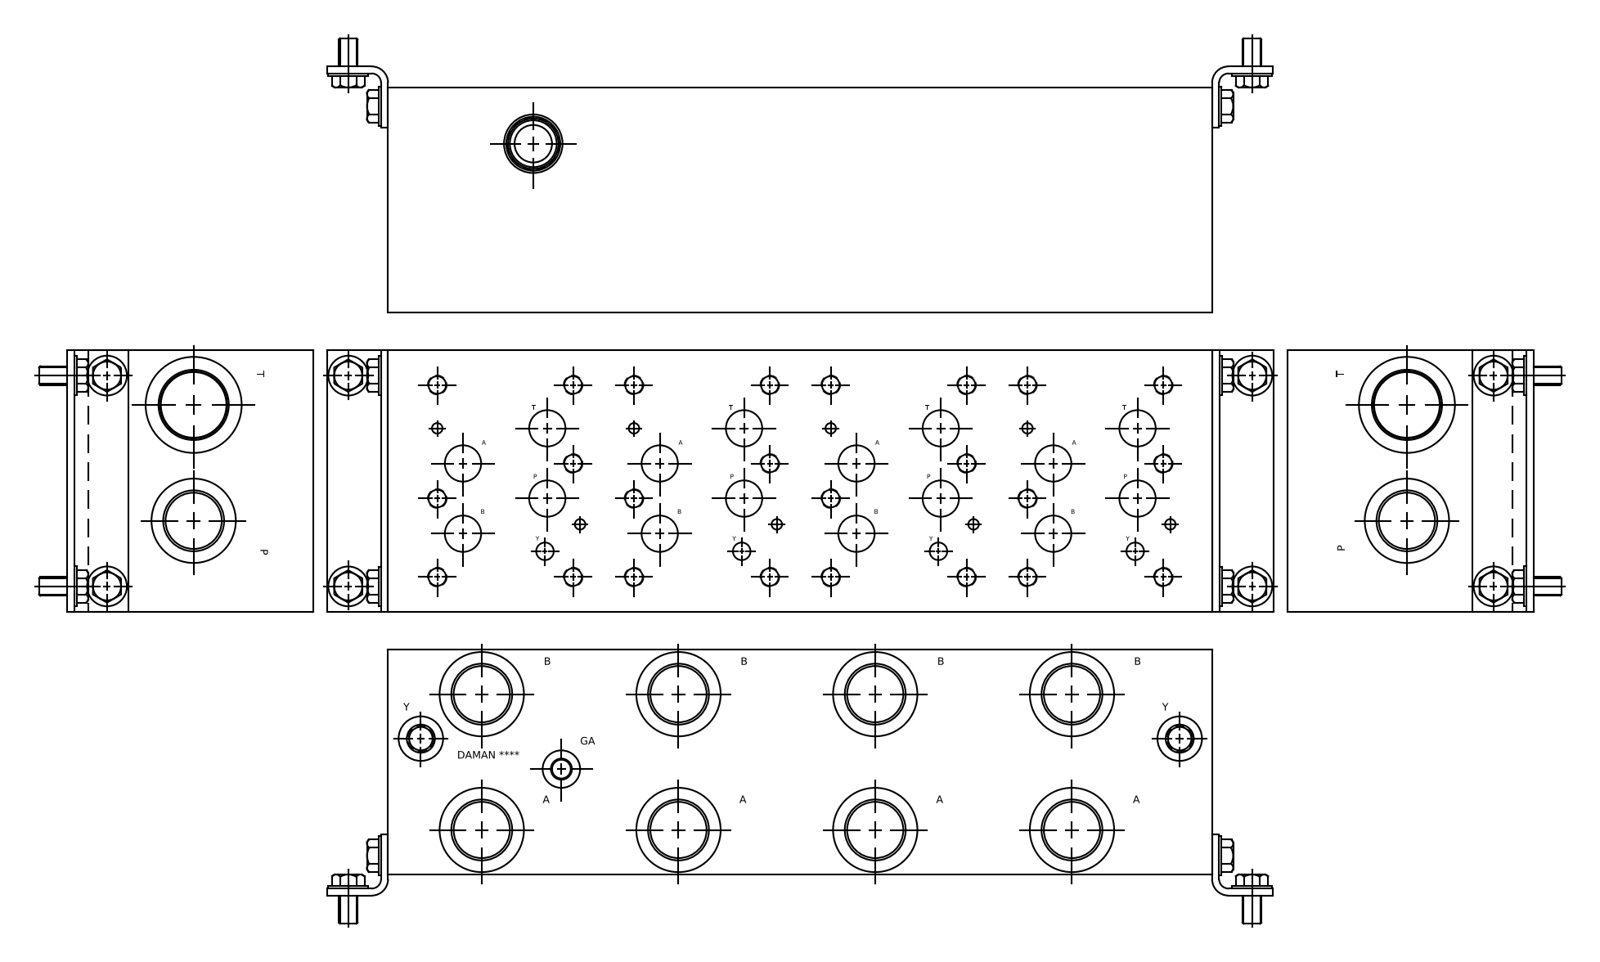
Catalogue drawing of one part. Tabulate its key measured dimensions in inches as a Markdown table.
| quantity | value |
| --- | --- |
| part name | Part_AD08HP045S~S_3D |
| STEP written by | Autodesk Inventor 2019 (AUTOMOTIVE_DESIGN) |
| units | inches |
| bodies | 1 solid, 977 faces (485 planar, 171 cylindrical, 321 other) |
| overall size | 22 × 7 × 6 |
| volume | 867.1 in³ |
| surface area | 853.7 in² |
| round holes (diameter × count) | 0.5 × 27, 0.422 × 26, 0.906 × 16, 1.544 × 9, 2.306 × 9, 0.281 × 8, 1.453 × 8, 1.625 × 8, 1.713 × 8, 0.438 × 4, 0.625 × 2, 0.689 × 2 |
| main face-to-face distances | 6, 7, 22, 0.031, 6.969, 21.969, 21.938, 0.75, 0.781, 6.219 |
| hole center spacings | 5.25, 10.5, 7.558, 2.438, 10.666, 15.75, 3.143, 5.575 |
